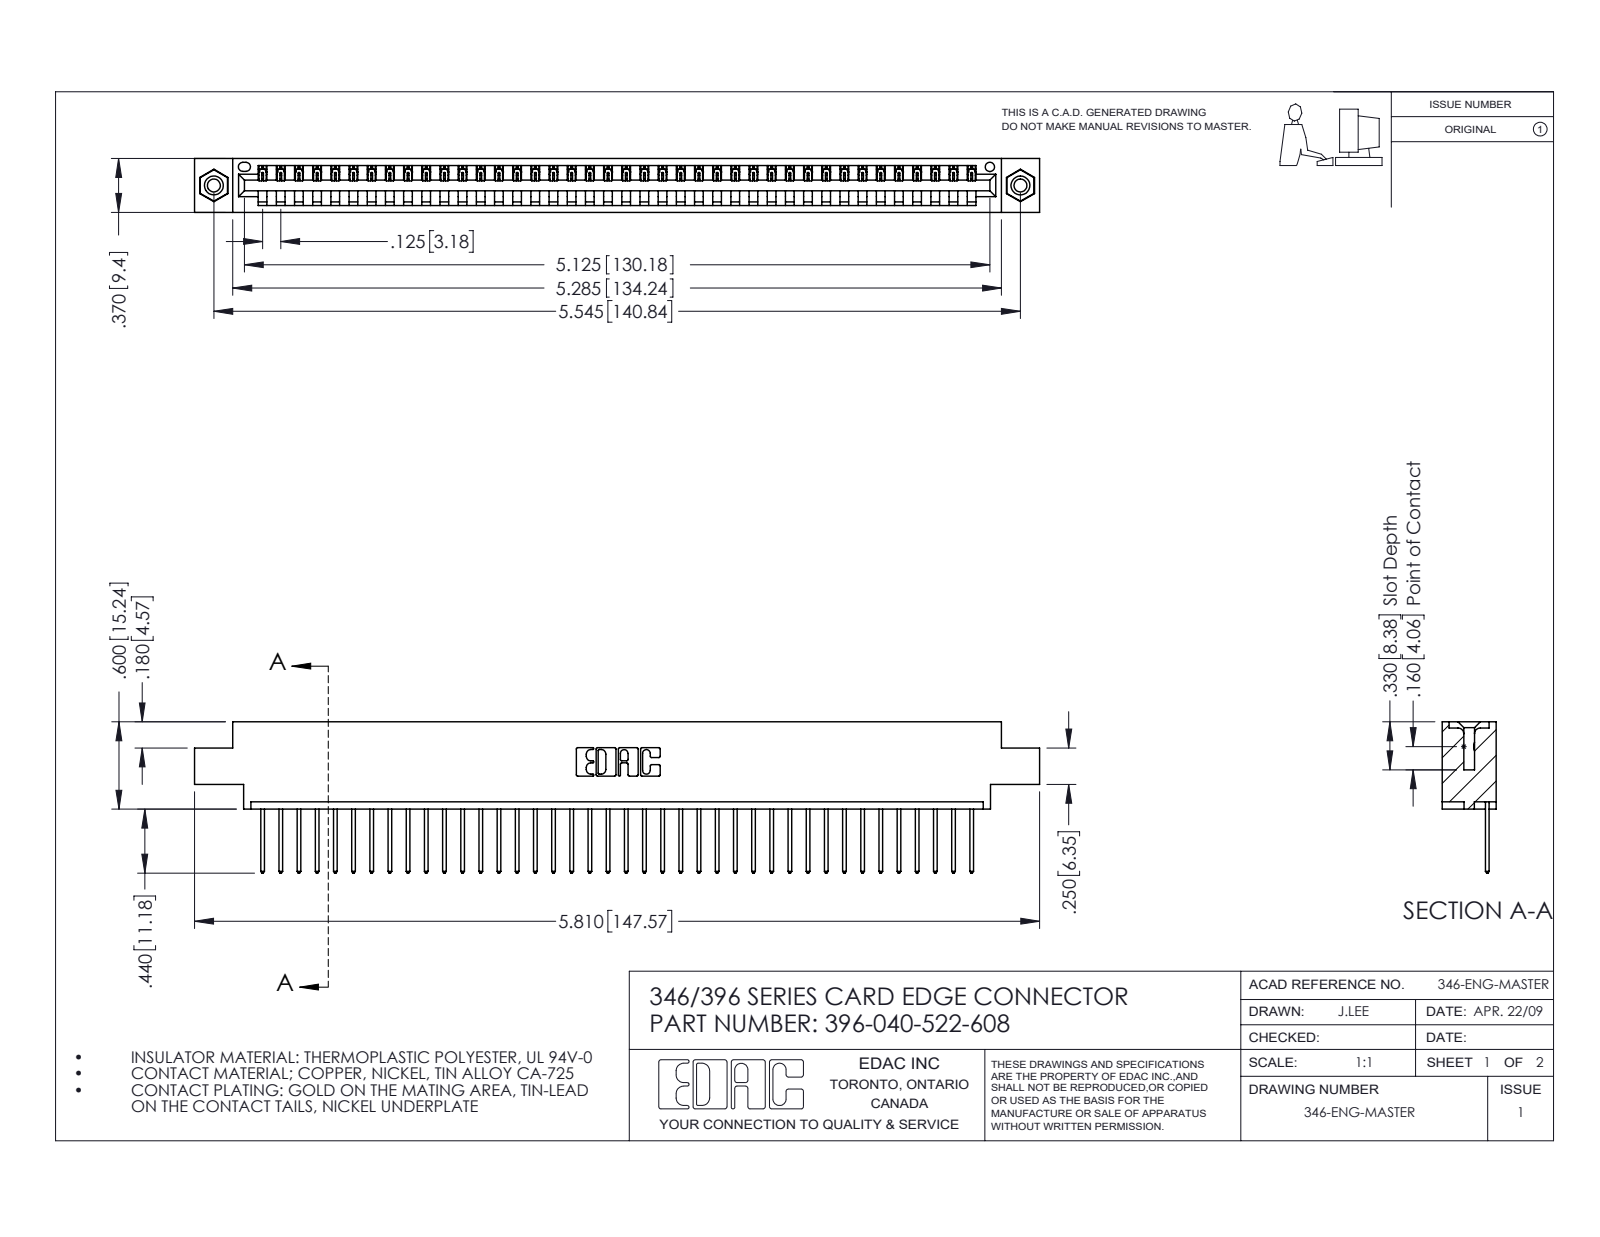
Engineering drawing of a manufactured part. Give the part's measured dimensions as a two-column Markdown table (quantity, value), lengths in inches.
| quantity | value |
| --- | --- |
| part name | 346 Part_0.170 Offset - 0.156 Dia-TI; 345-250-001_345-250-003-102; 396-040-522-608; 345-292-001_345-293-122 |
| STEP written by | SolidWorks 2016 (CONFIG_CONTROL_DESIGN) |
| units | inches |
| bodies | 43 solids, 2506 faces (1712 planar, 778 cylindrical, 16 other) |
| overall size | 5.81 × 1.04 × 0.37 |
| volume | 0.852 in³ |
| surface area | 27.51 in² |
| round holes (diameter × count) | 0.089 × 2, 0.125 × 2, 0.156 × 2, 0.064 × 1 |
| round bosses / shafts (diameter × count) | 0.155 × 2 |
| partial cylindrical surfaces (radius × count) | 0.006 × 80, 0.01 × 80, 0.01 × 22, 0.007 × 6, 0.031 × 6, 0.026 × 3, 0.031 × 2, 0.04 × 2 |
| main face-to-face distances | 0.048, 0.322, 0.37, 0.25, 0.072, 0.298, 0.025, 0.222, 0.148, 0.1 |
| hole center spacings | 0.246, 5.336, 5.545 |
